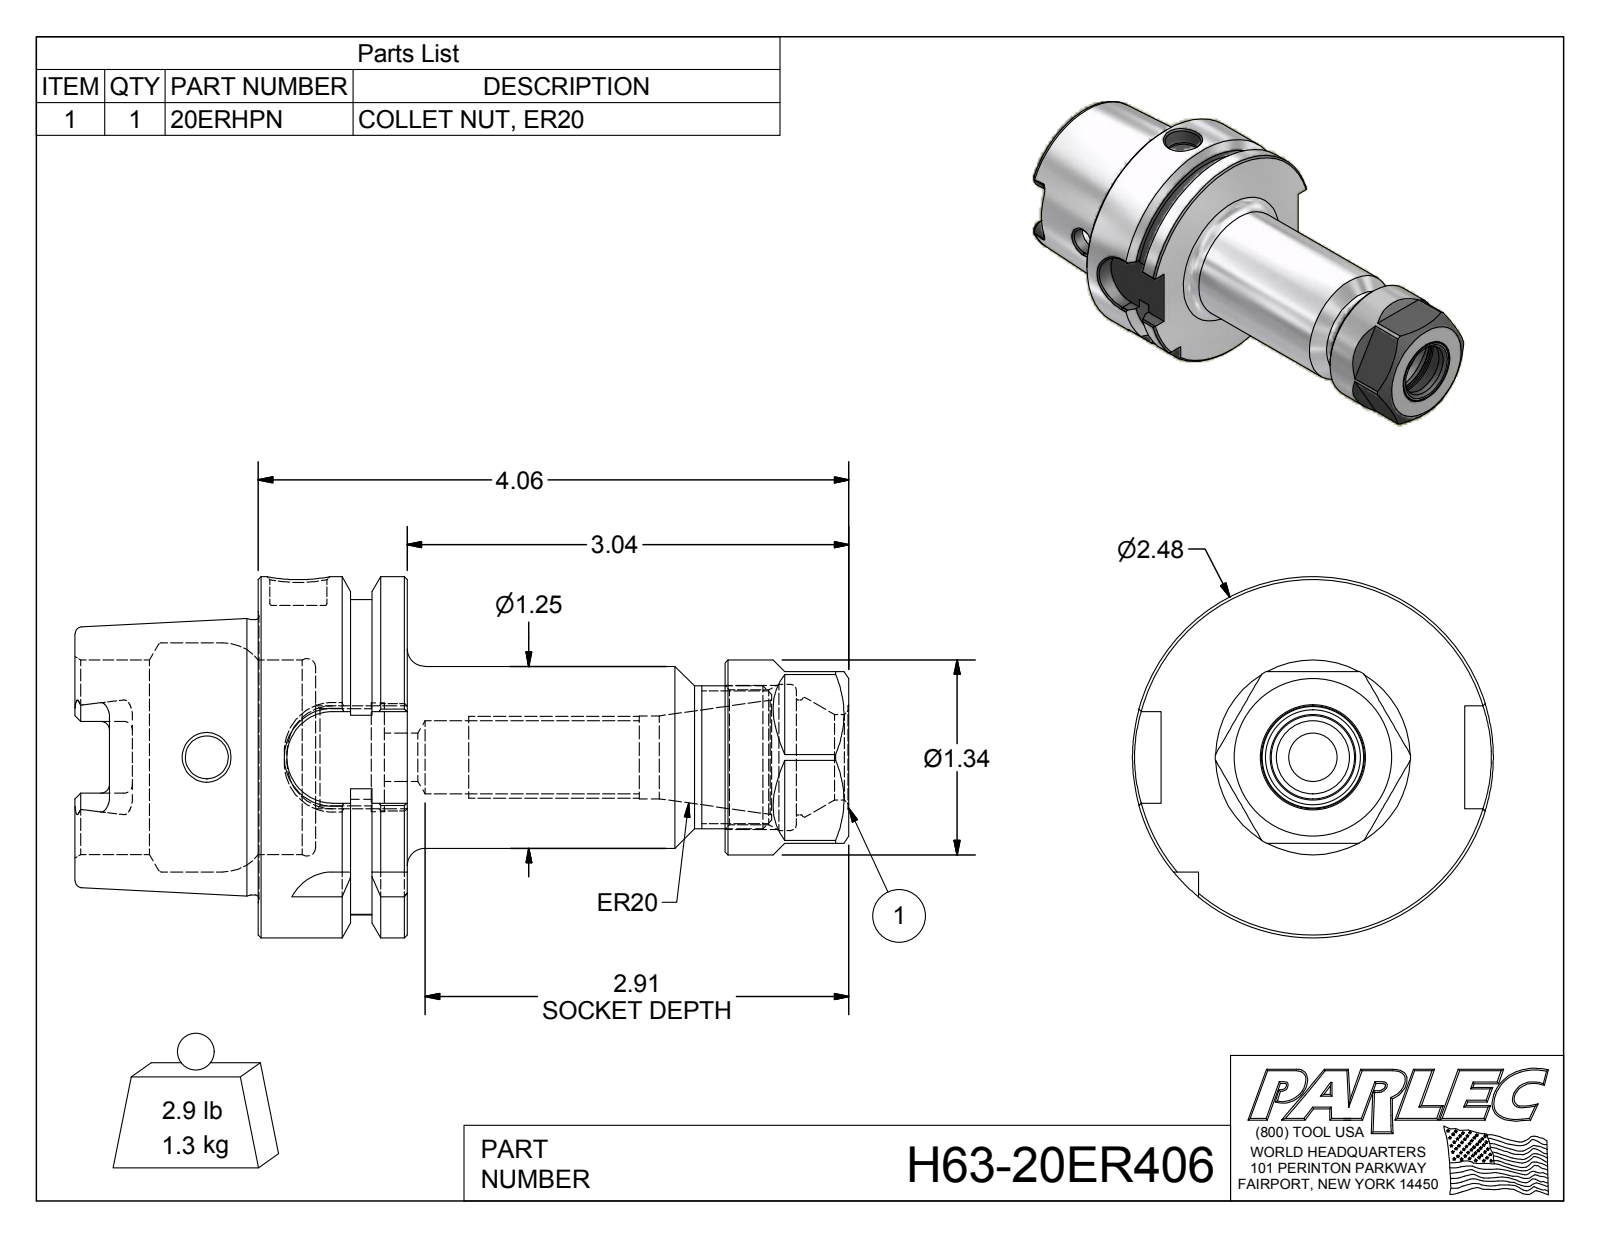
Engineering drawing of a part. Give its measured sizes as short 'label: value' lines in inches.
name: H63-20ER406; H63-20ER4-1; 20ERHPN
written by: Autodesk Inventor 2012 (AUTOMOTIVE_DESIGN)
unit: in
bodies: 2 solids, 171 faces (68 planar, 41 cylindrical, 62 other)
size: 5.32 × 2.48 × 2.48
volume: 7.733 in³; area: 55.32 in²
holes: 1× ⌀0.295, 1× ⌀0.335, 1× ⌀0.394, 1× ⌀0.502, 1× ⌀0.57, 1× ⌀0.587, 1× ⌀0.666, 1× ⌀0.749, 1× ⌀0.79, 1× ⌀0.926, 1× ⌀1.005, 1× ⌀1.339
bosses: 1× ⌀2.48, 1× ⌀1.891, 1× ⌀1.34, 1× ⌀1.25, 1× ⌀0.984
rounds: 6× R0.059, 4× R0.113, 4× R0.315, 1× R1.083
face distances: 1.024, 0.241, 0.389, 0.394, 0.63, 1.18, 1.26, 1.654, 2.283, 4.47
